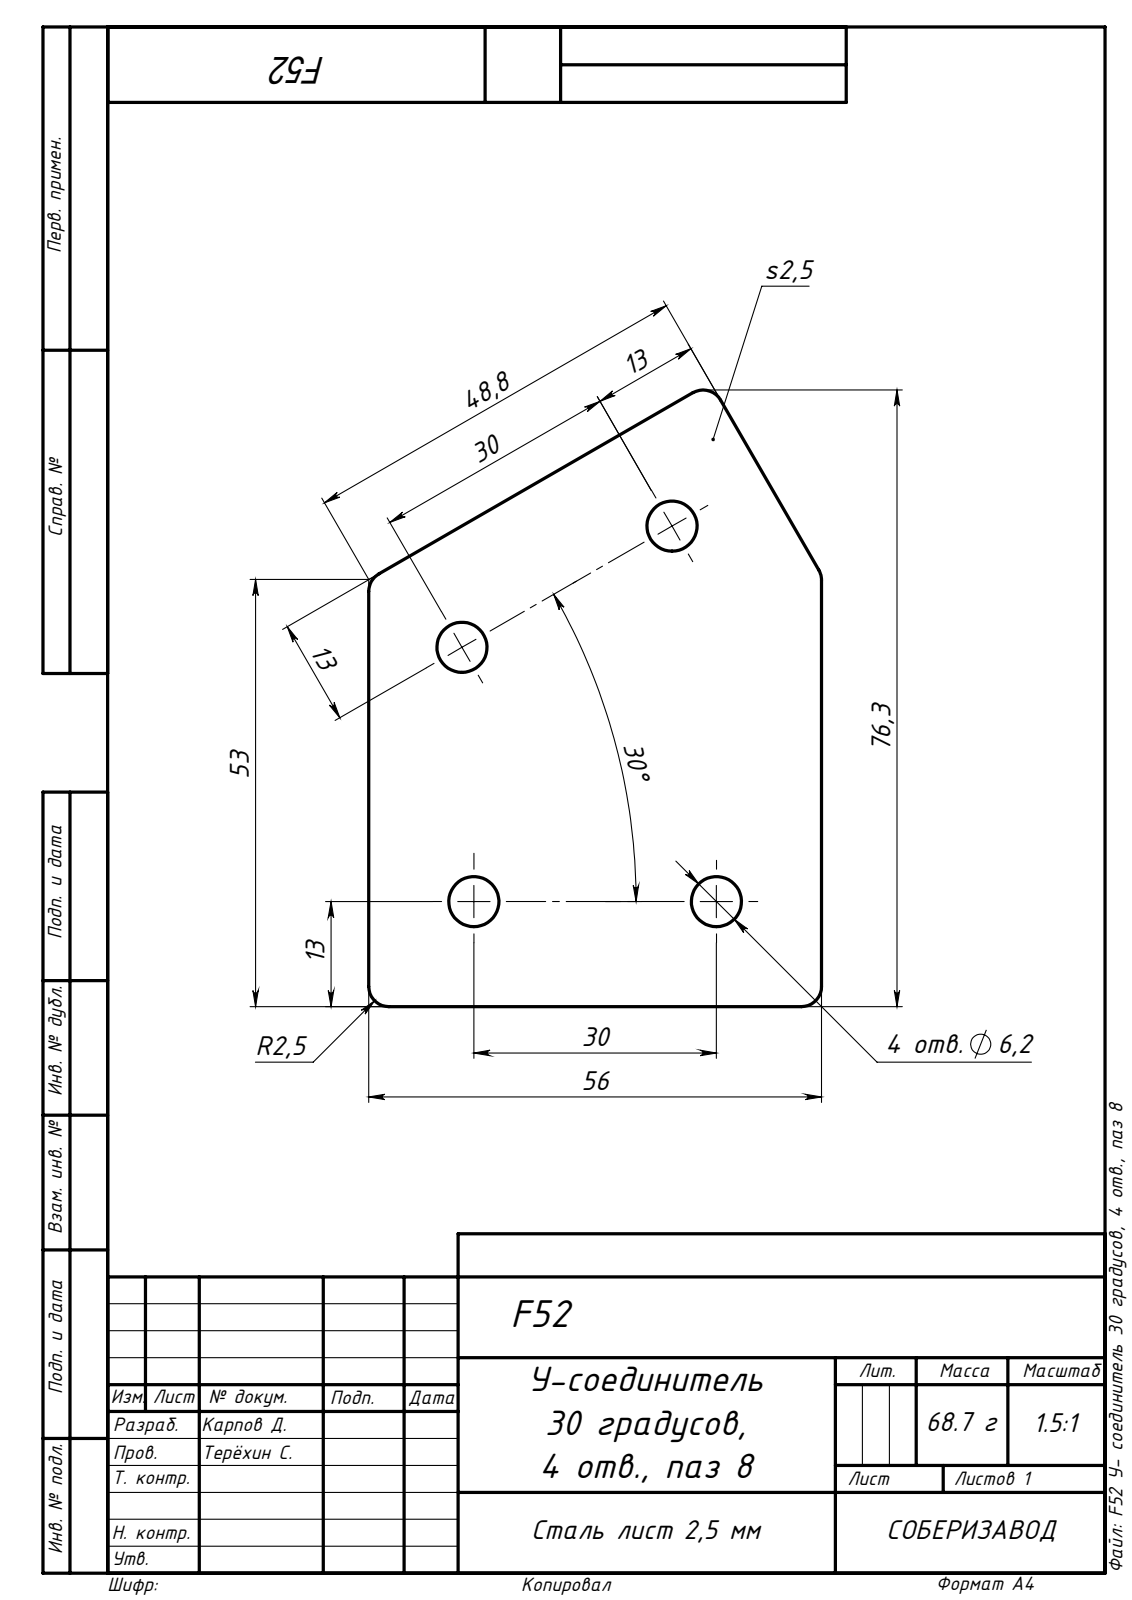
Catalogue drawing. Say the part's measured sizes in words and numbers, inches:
The part is named "F52 У- соединитель 30 градусов, 4 отв., паз 8". Its 3-D file was written by "SolidWorks 2020 (AUTOMOTIVE_DESIGN)". It is 1 solid with 20 faces: 7 planar, 13 cylindrical and 0 other. Overall it measures 3.004 by 2.205 by 0.098 inches. Its volume is 0.537 cubic inches and its surface area 12.13 square inches. Round holes: 4 of diameter 0.244. Partial cylindrical surfaces (rounded edges, fillets, slot ends): 5 of radius 0.098. The main face-to-face distances are 0.098, 2.205. The hole center spacings are 1.181, 1.24, 1.752, 1.842, 2.069.
